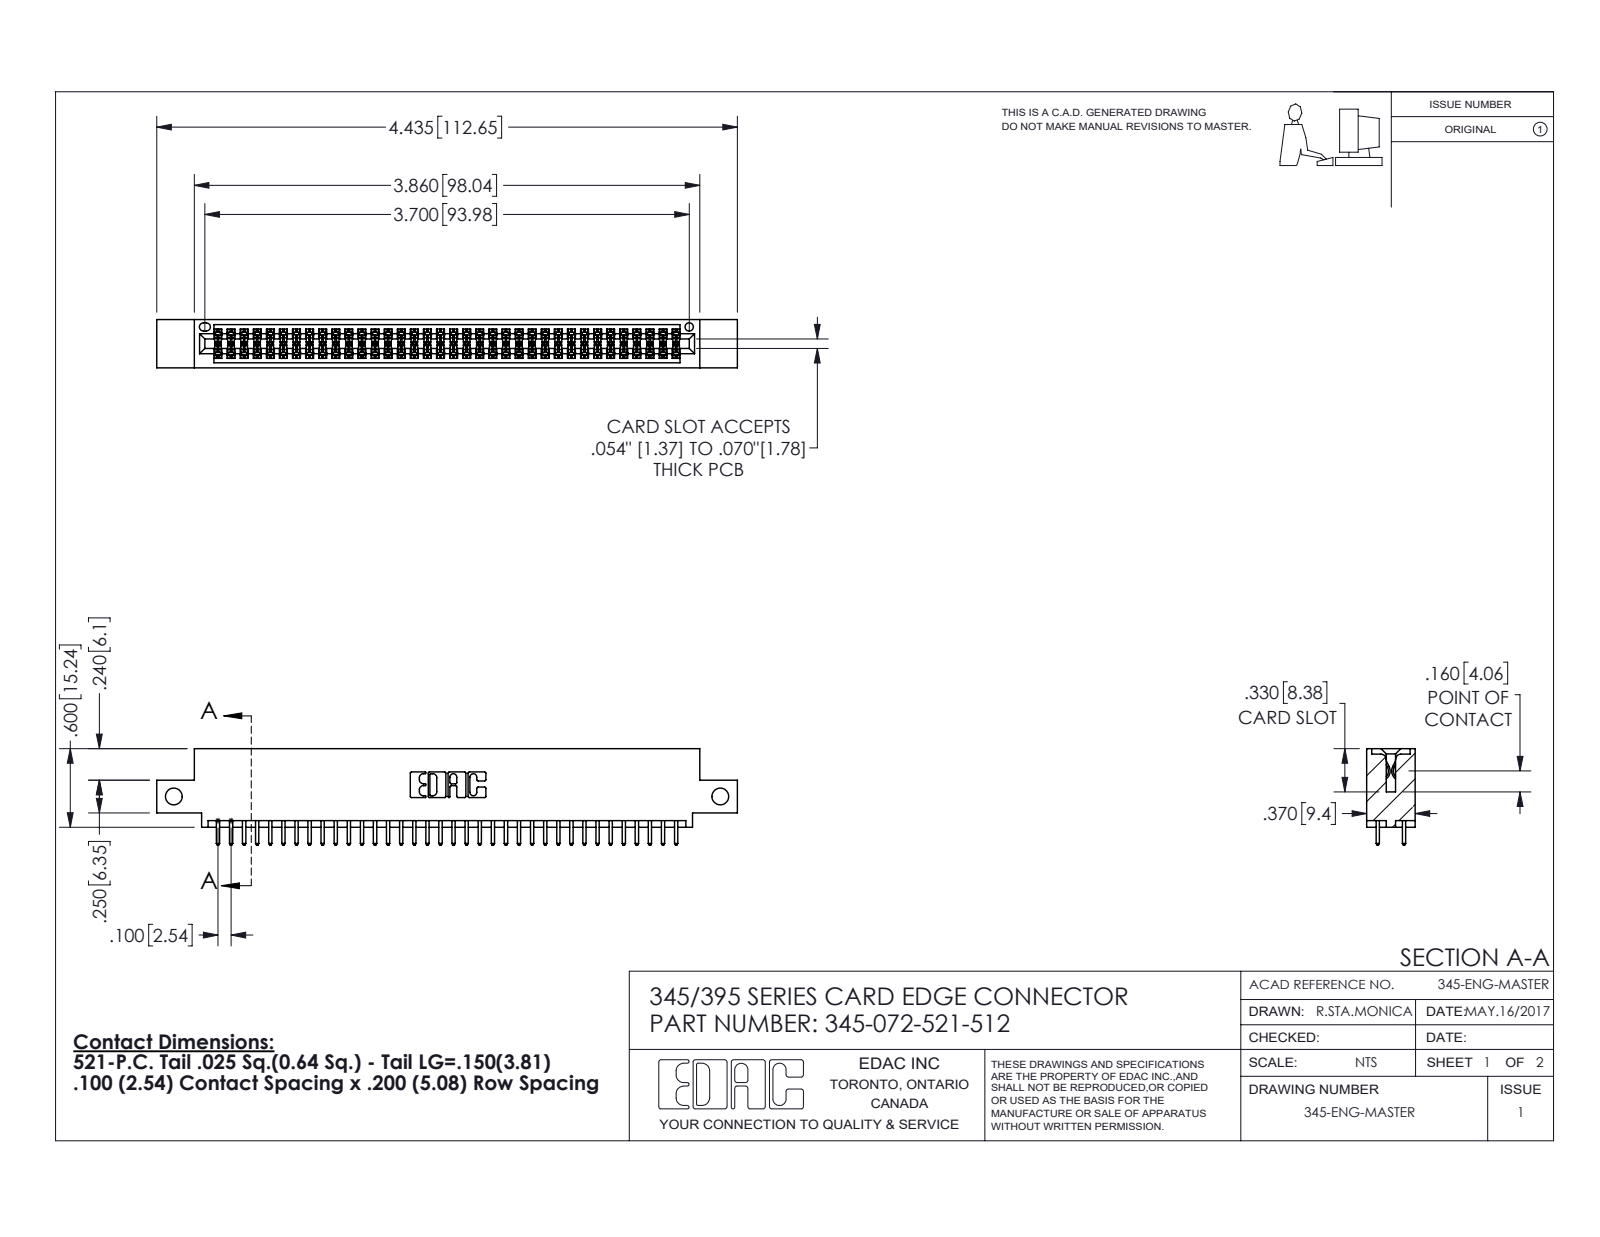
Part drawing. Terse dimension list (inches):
name: 345-072-521-512; 345-292-001_345-293-121; 345 Part_0.110 Offset - Side Mount
written by: SolidWorks 2016 (CONFIG_CONTROL_DESIGN)
unit: in
bodies: 73 solids, 3730 faces (2460 planar, 1270 cylindrical, 0 other)
size: 4.435 × 0.737 × 0.37
volume: 0.653 in³; area: 23.97 in²
holes: 2× ⌀0.128, 1× ⌀0.064
rounds: 108× R0.006, 72× R0.01, 22× R0.01, 6× R0.007, 6× R0.031, 3× R0.026, 2× R0.014, 2× R0.019
face distances: 0.298, 0.072, 0.2, 0.37, 0.098, 0.272, 0.025, 0.225, 0.175, 0.149
hole spacings: 4.175
